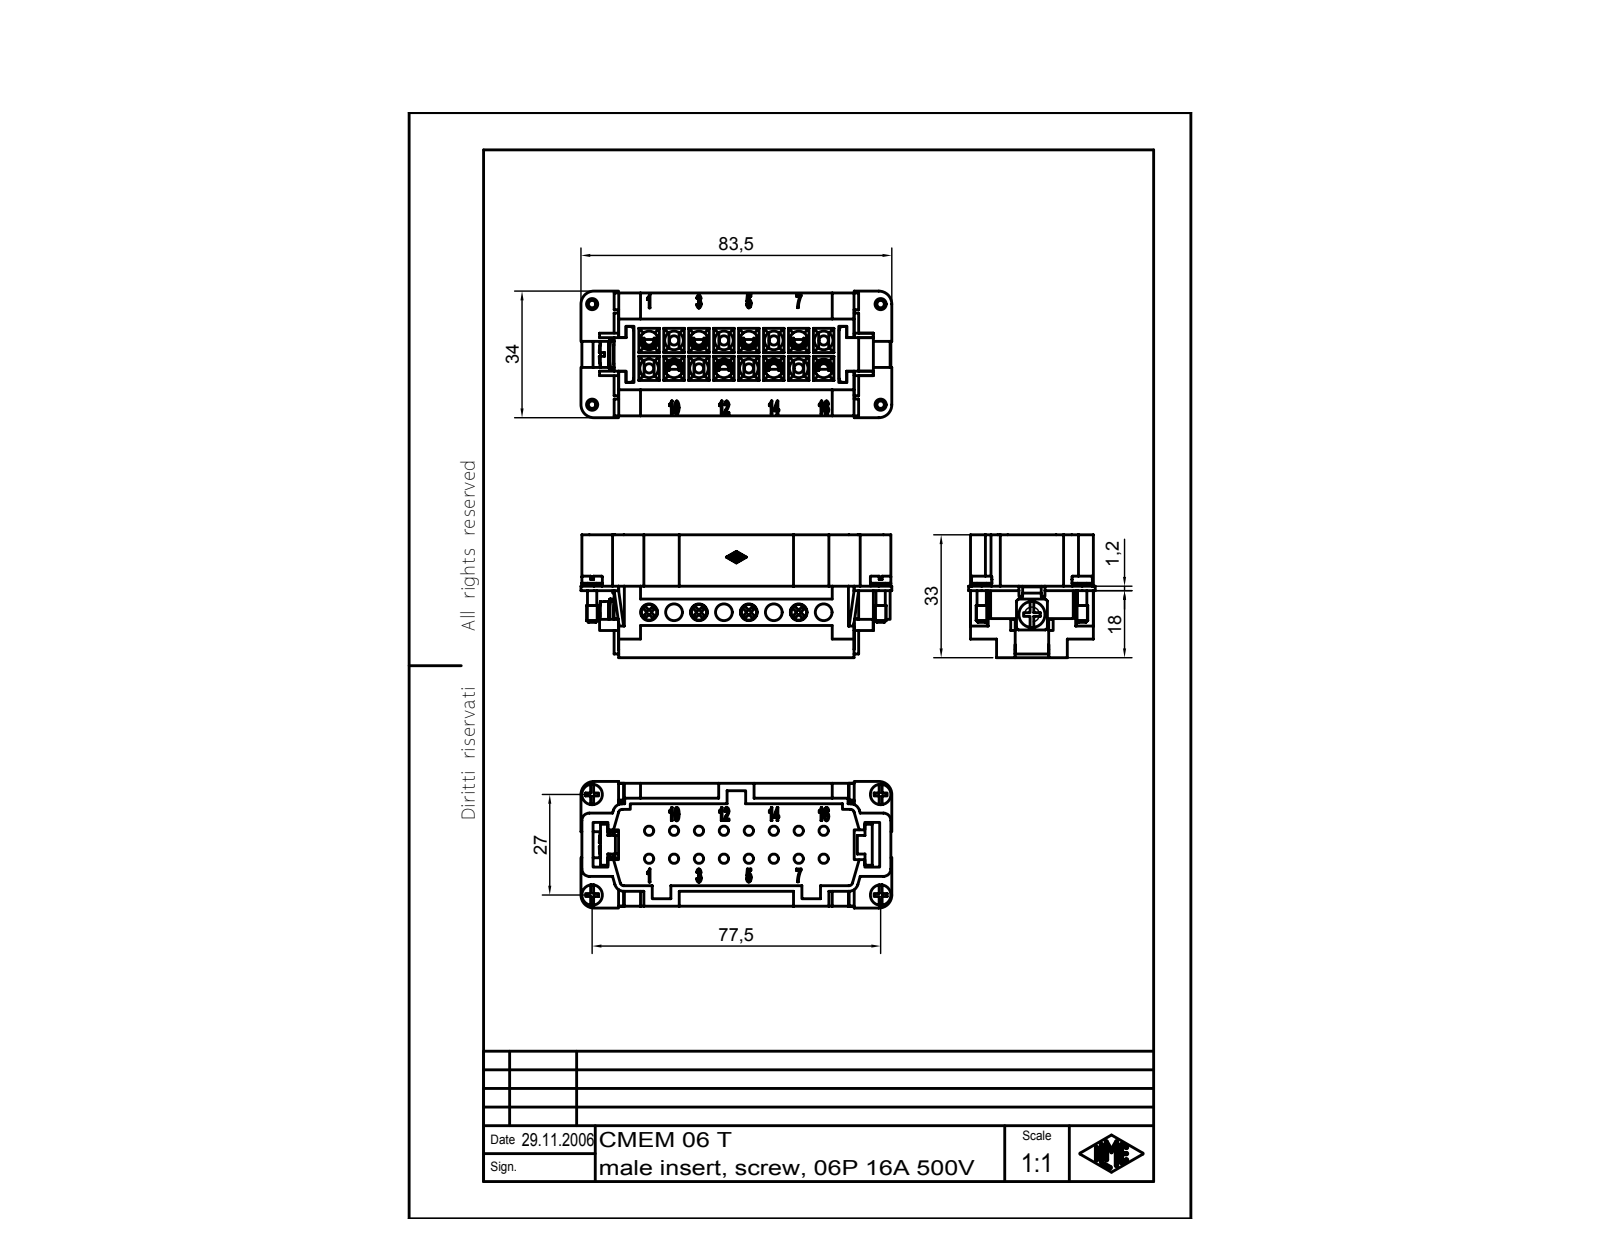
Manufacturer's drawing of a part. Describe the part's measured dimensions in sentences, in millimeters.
The part is named "CMEM 06 T". Its 3-D file was written by "Autodesk Inventor 7 (AUTOMOTIVE_DESIGN)". It is 9 solids with 1419 faces: 724 planar, 229 cylindrical and 466 other. Overall it measures 83.5 by 34 by 33 millimeters. Its volume is 33 063 cubic millimeters and its surface area 29 983 square millimeters. Round holes: 8 of diameter 2.5, 8 of diameter 3, 8 of diameter 4.5, 8 of diameter 5, 2 of diameter 2.55. Round bosses or shafts: 8 of diameter 4.2, 6 of diameter 2.5, 2 of diameter 5.5, 2 of diameter 5.3, 2 of diameter 3, 1 of diameter 7. Partial cylindrical surfaces (rounded edges, fillets, slot ends): 14 of radius 0.1, 8 of radius 2.1, 6 of radius 1, 6 of radius 2, 4 of radius 2.5, 2 of radius 3.5, 1 of radius 1.62, 1 of radius 5.5. The main face-to-face distances are 1.5, 22, 3, 20.5, 4, 5.5, 23.5, 29, 7, 1. The hole center spacings are 6.7, 13.4, 20.1, 10.06, 15.36, 26.8, 21.45, 33.5.
